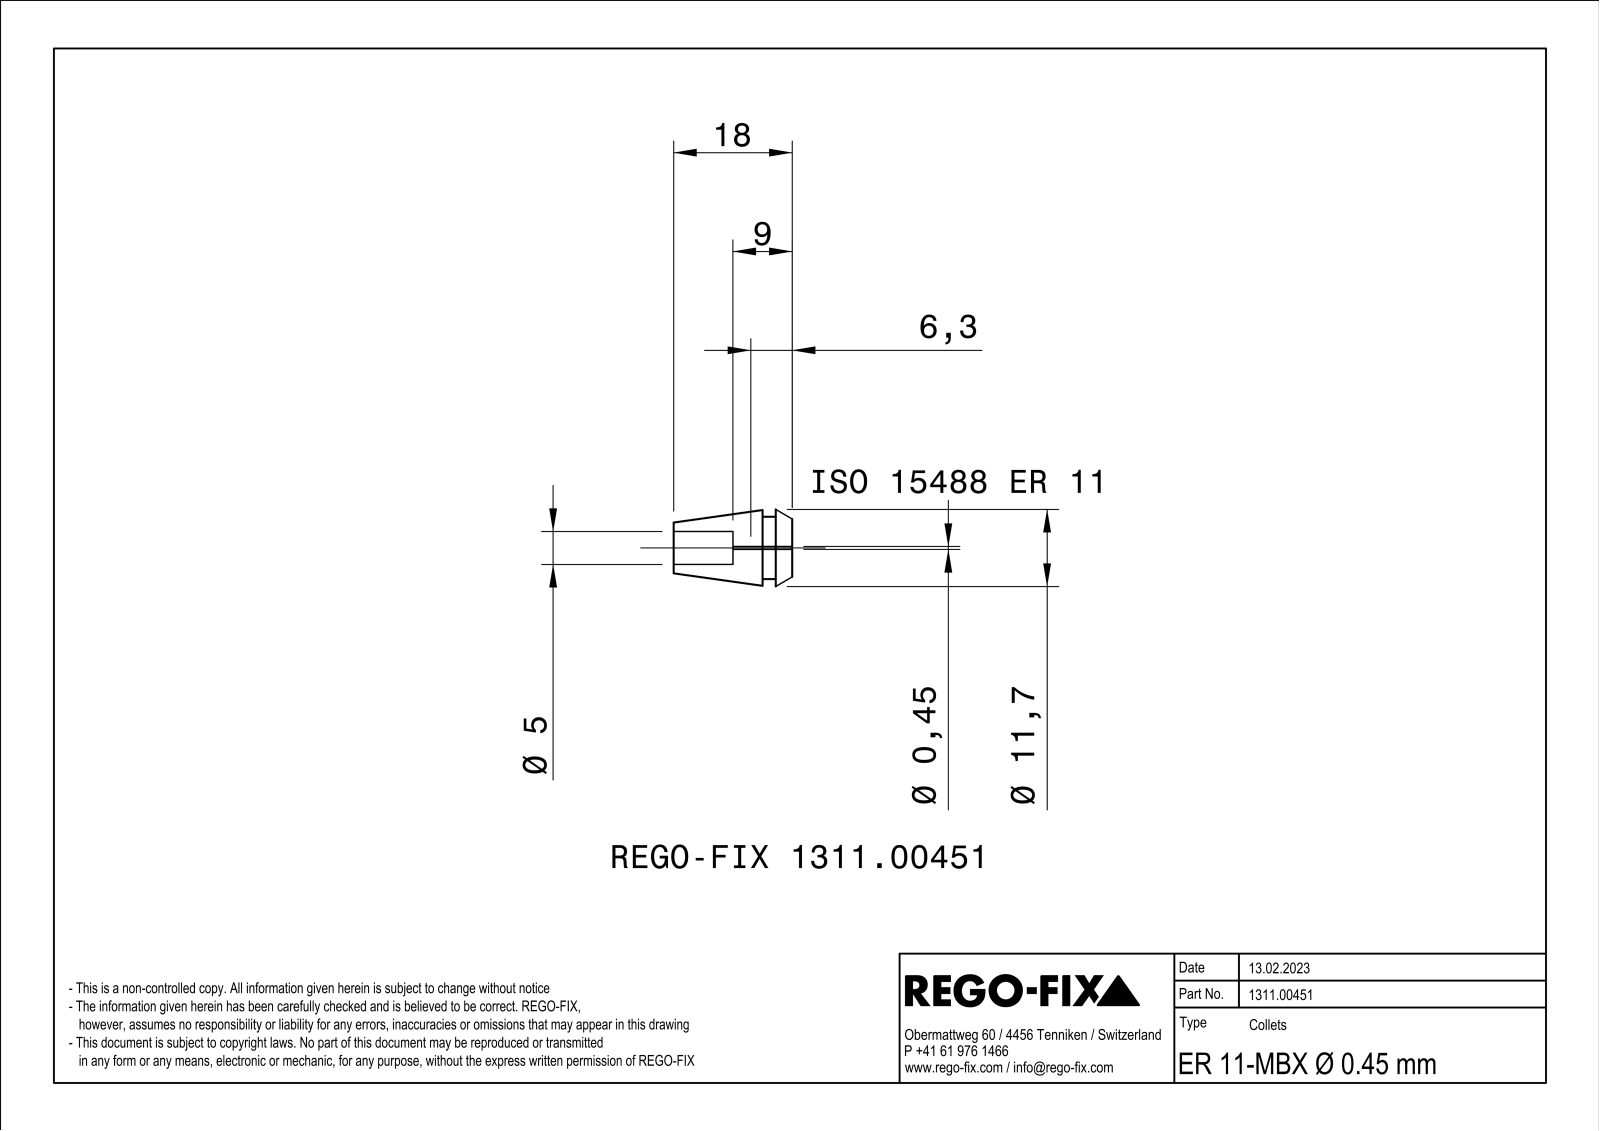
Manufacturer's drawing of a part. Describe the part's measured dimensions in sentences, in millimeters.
The part is named "NOCUT". Its 3-D file was written by "SIEMENS PLM Software Solid Edge ST10 (AUTOMOTIVE_DESIGN)". It is 1 solid with 91 faces: 26 planar, 19 cylindrical and 46 other. Overall it measures 18 by 11.41 by 11.39 millimeters. Its volume is 992 cubic millimeters and its surface area 1 256 square millimeters. Round holes: 3 of diameter 1.5, 1 of diameter 5. Round bosses or shafts: 1 of diameter 9.5. Partial cylindrical surfaces (rounded edges, fillets, slot ends): 3 of radius 25, 1 of radius 0.23. The main face-to-face distances are 0.8, 0.51, 4.5, 9, 18, 13.5, 2.5, 2, 15.5, 6.5. The hole center spacings are 1.7, 2.94.
